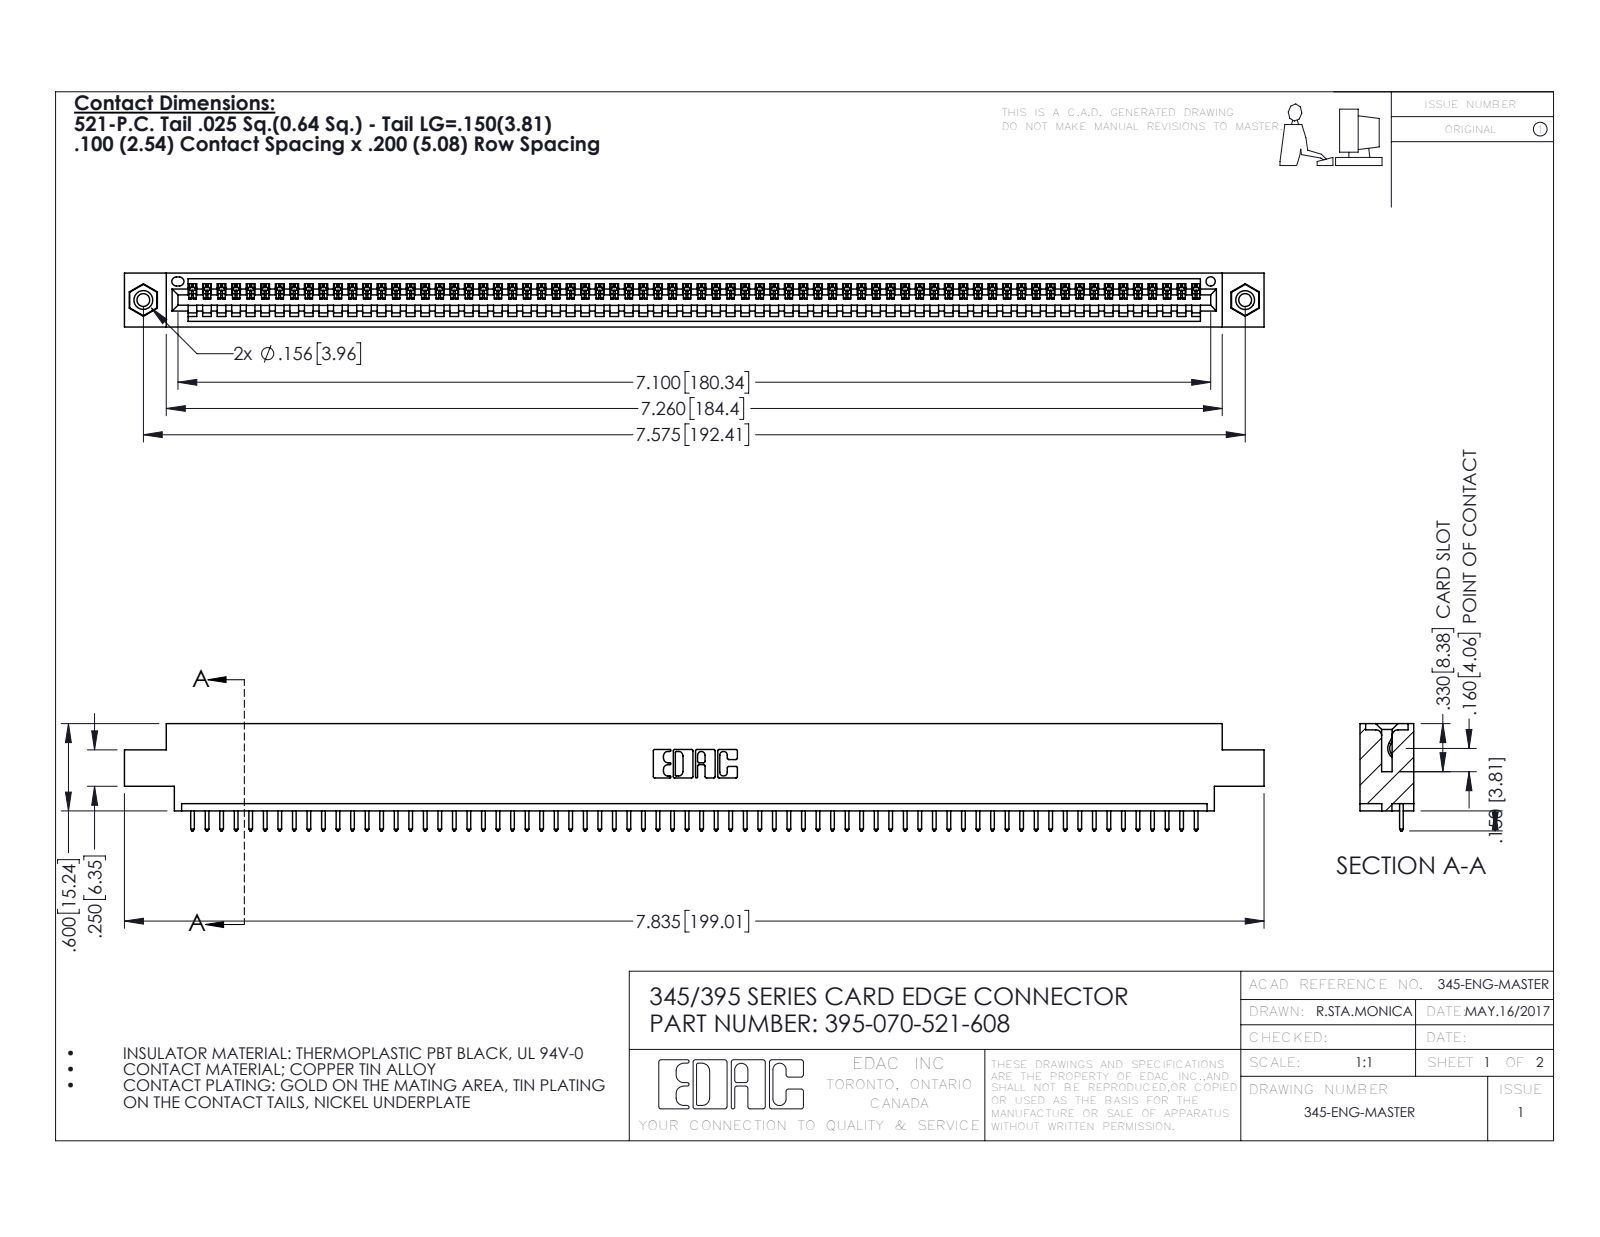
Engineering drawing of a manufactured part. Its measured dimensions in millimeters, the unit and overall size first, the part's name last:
Units: millimetres
Overall size (bounding box): 199 × 18.7 × 9.4
Round holes (diameter × count): ⌀2.3 ×2, ⌀3.2 ×2, ⌀4 ×2, ⌀1.6 ×1
Round bosses / shafts (diameter × count): ⌀3.9 ×2
Partial cylindrical surfaces — rounded edges, fillets, slot ends (radius × count): R0.2 ×140, R0.3 ×140, R0.3 ×22, R0.2 ×6, R0.8 ×6, R0.7 ×3, R0.8 ×2, R1 ×2
Main face-to-face distances: 1.8, 7.6, 9.4, 5.1, 2.5, 6.9, 0.6, 5.7, 4.4, 3.8
Hole centre spacings: 6.9, 186.4, 192.4
Volume: 18 810 mm³ · Surface area: 24 750 mm²
Bodies: 73 solids, 4250 faces (2916 planar, 1318 cylindrical, 16 other)
Part name (STEP PRODUCT): 395-070-521-608; 345 Part_0.170 Offset - 0.156 Dia-TI; 345-292-001_345-293-121; 345-250-001_345-250-003-102
STEP written by: SolidWorks 2016 (CONFIG_CONTROL_DESIGN)
